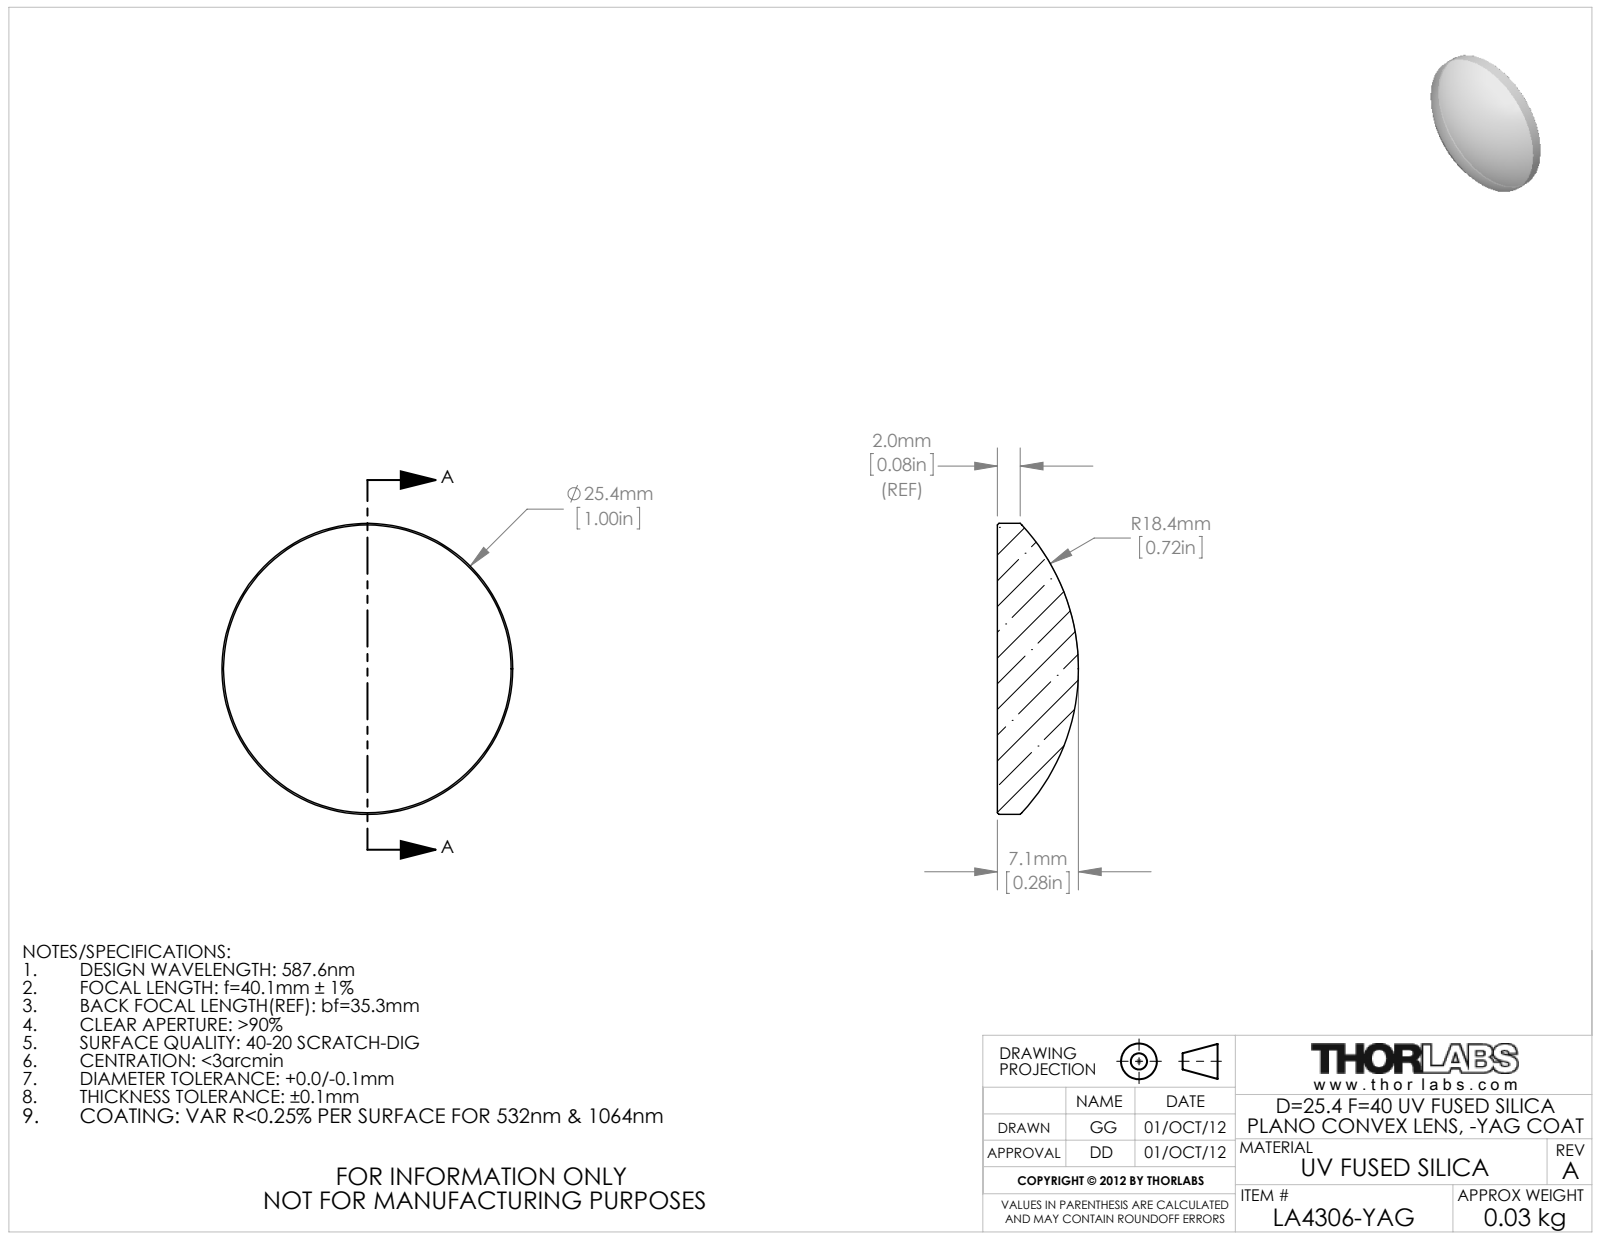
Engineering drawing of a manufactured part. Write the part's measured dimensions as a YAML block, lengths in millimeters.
part_name: "24954-E0W"
step_written_by: "SolidWorks 2011 (CONFIG_CONTROL_DESIGN)"
units: millimeters
bodies: {solids: 1, faces: 9, planar: 1, cylindrical: 2, other: 6}
overall_size: [25.4, 25.4, 7.08]
volume: 2369
surface_area: 1247
round_bosses_or_shafts:
  - {diameter: 25.4, count: 1}
